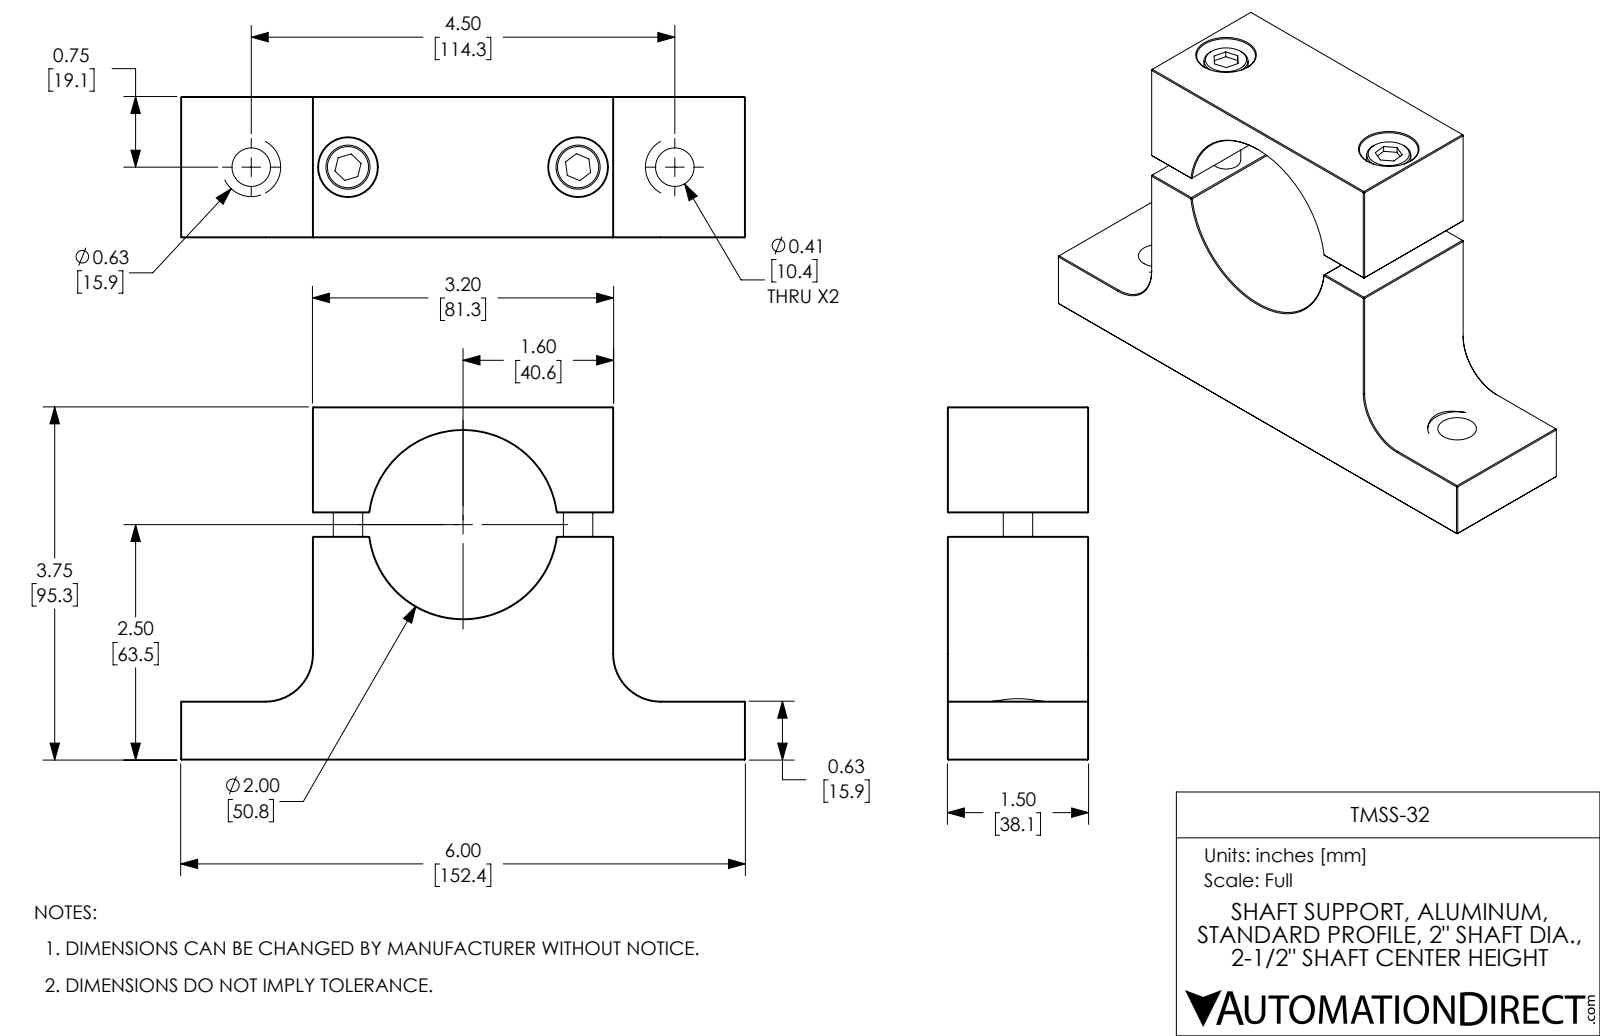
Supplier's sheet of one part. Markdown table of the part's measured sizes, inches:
| quantity | value |
| --- | --- |
| part name | TMSS-32 |
| STEP written by | SolidWorks 2017 (AUTOMOTIVE_DESIGN) |
| units | inches |
| bodies | 4 solids, 164 faces (110 planar, 30 cylindrical, 24 other) |
| overall size | 6 × 3.75 × 1.5 |
| volume | 15.01 in³ |
| surface area | 73.37 in² |
| round holes (diameter × count) | 0.307 × 2, 0.397 × 2, 0.41 × 2, 0.625 × 2, 2 × 1 |
| round bosses / shafts (diameter × count) | 0.469 × 2, 0.313 × 2 |
| partial cylindrical surfaces (radius × count) | 0.313 × 2, 0.5 × 2 |
| main face-to-face distances | 1.5, 3.75, 3.2, 0.625, 3.125, 1.4, 4.6, 2.375, 1.75, 1.375 |
| hole center spacings | 1.028, 3.472, 2.445, 4.5 |
